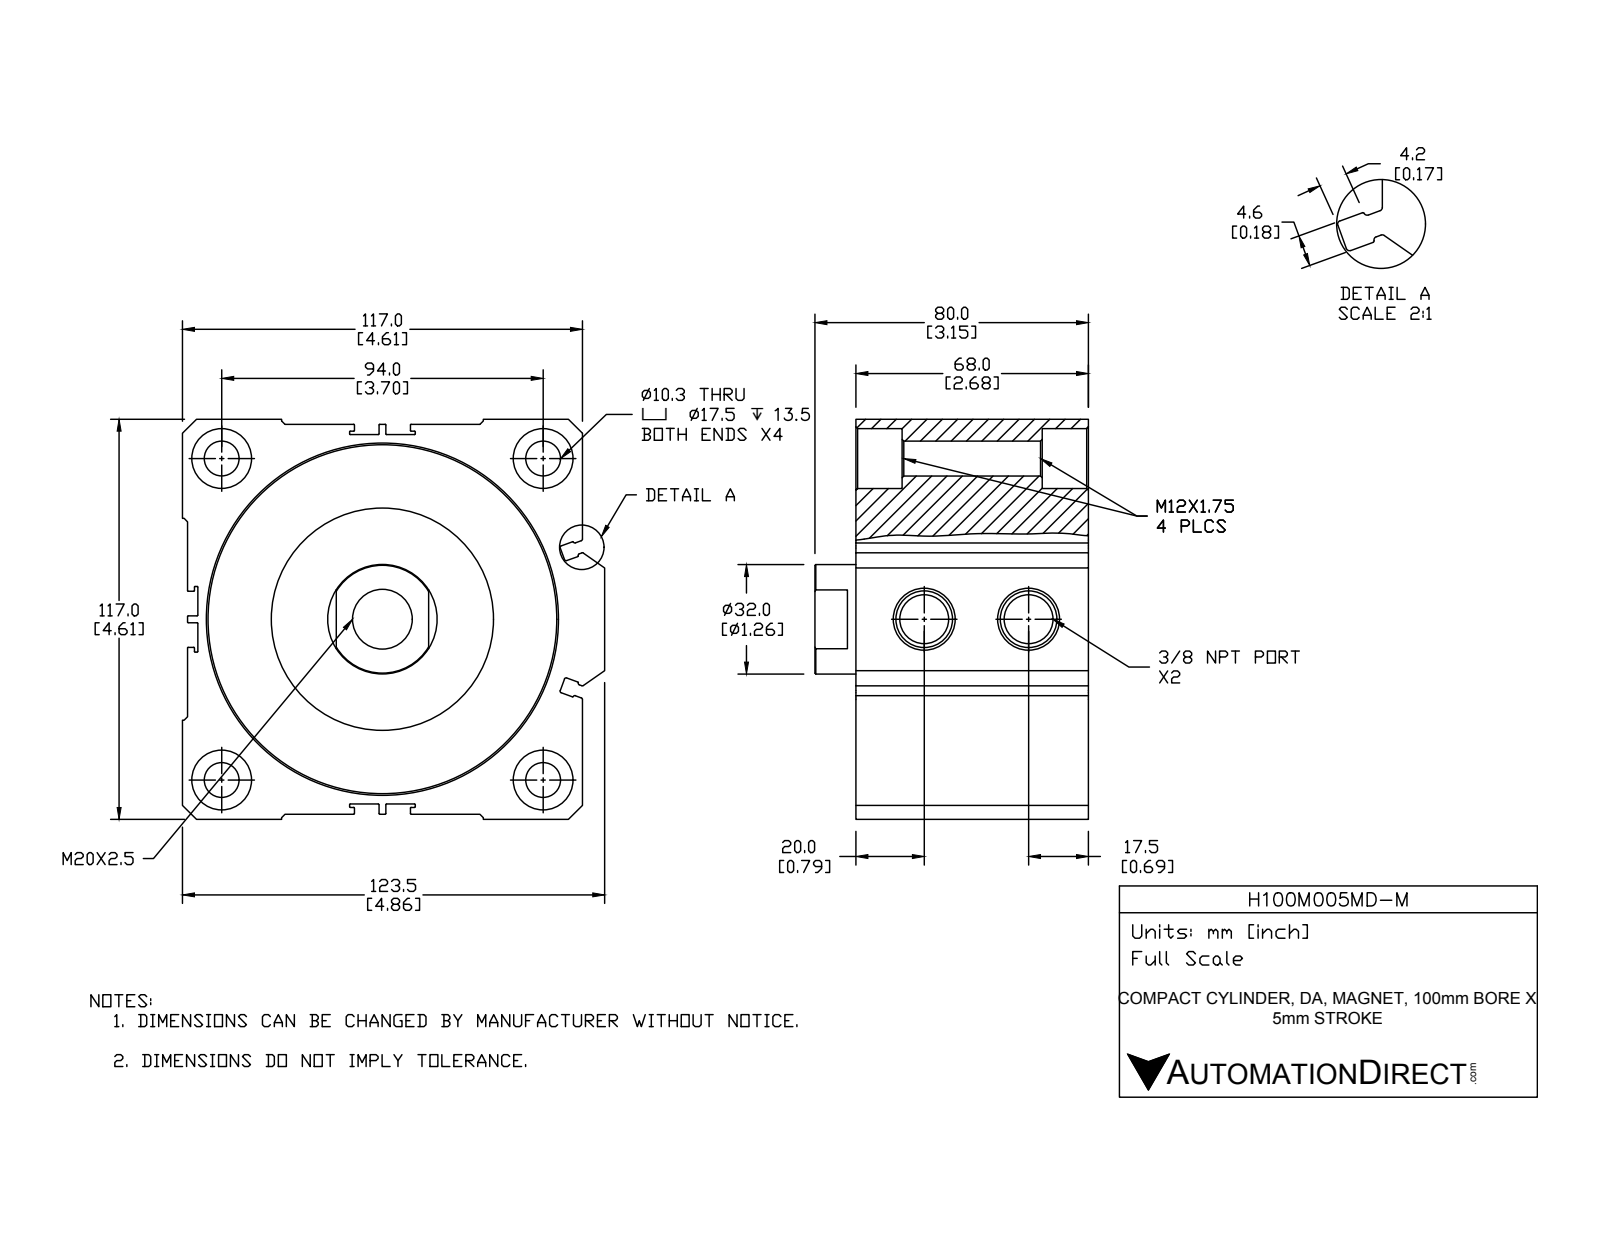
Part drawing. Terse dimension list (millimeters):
name: H100M005MD-M-PISTON; H100M005MD-M-BODY; H100M005MD-M
written by: SolidWorks 2015 (CONFIG_CONTROL_DESIGN)
unit: mm
bodies: 2 solids, 261 faces (105 planar, 103 cylindrical, 53 other)
size: 123.5 × 117 × 80
volume: 766 494 mm³; area: 137 782 mm²
holes: 5× ⌀17.5, 4× ⌀10.2, 2× ⌀14.27, 1× ⌀32, 1× ⌀65, 1× ⌀100, 1× ⌀102
bosses: 1× ⌀39
rounds: 40× R0.2, 12× R0.5
face distances: 1.5, 115.5, 27.8, 33.5, 5.7, 117, 12.5, 40.3, 46, 58
hole spacings: 66.47, 94, 132.94, 30.5
